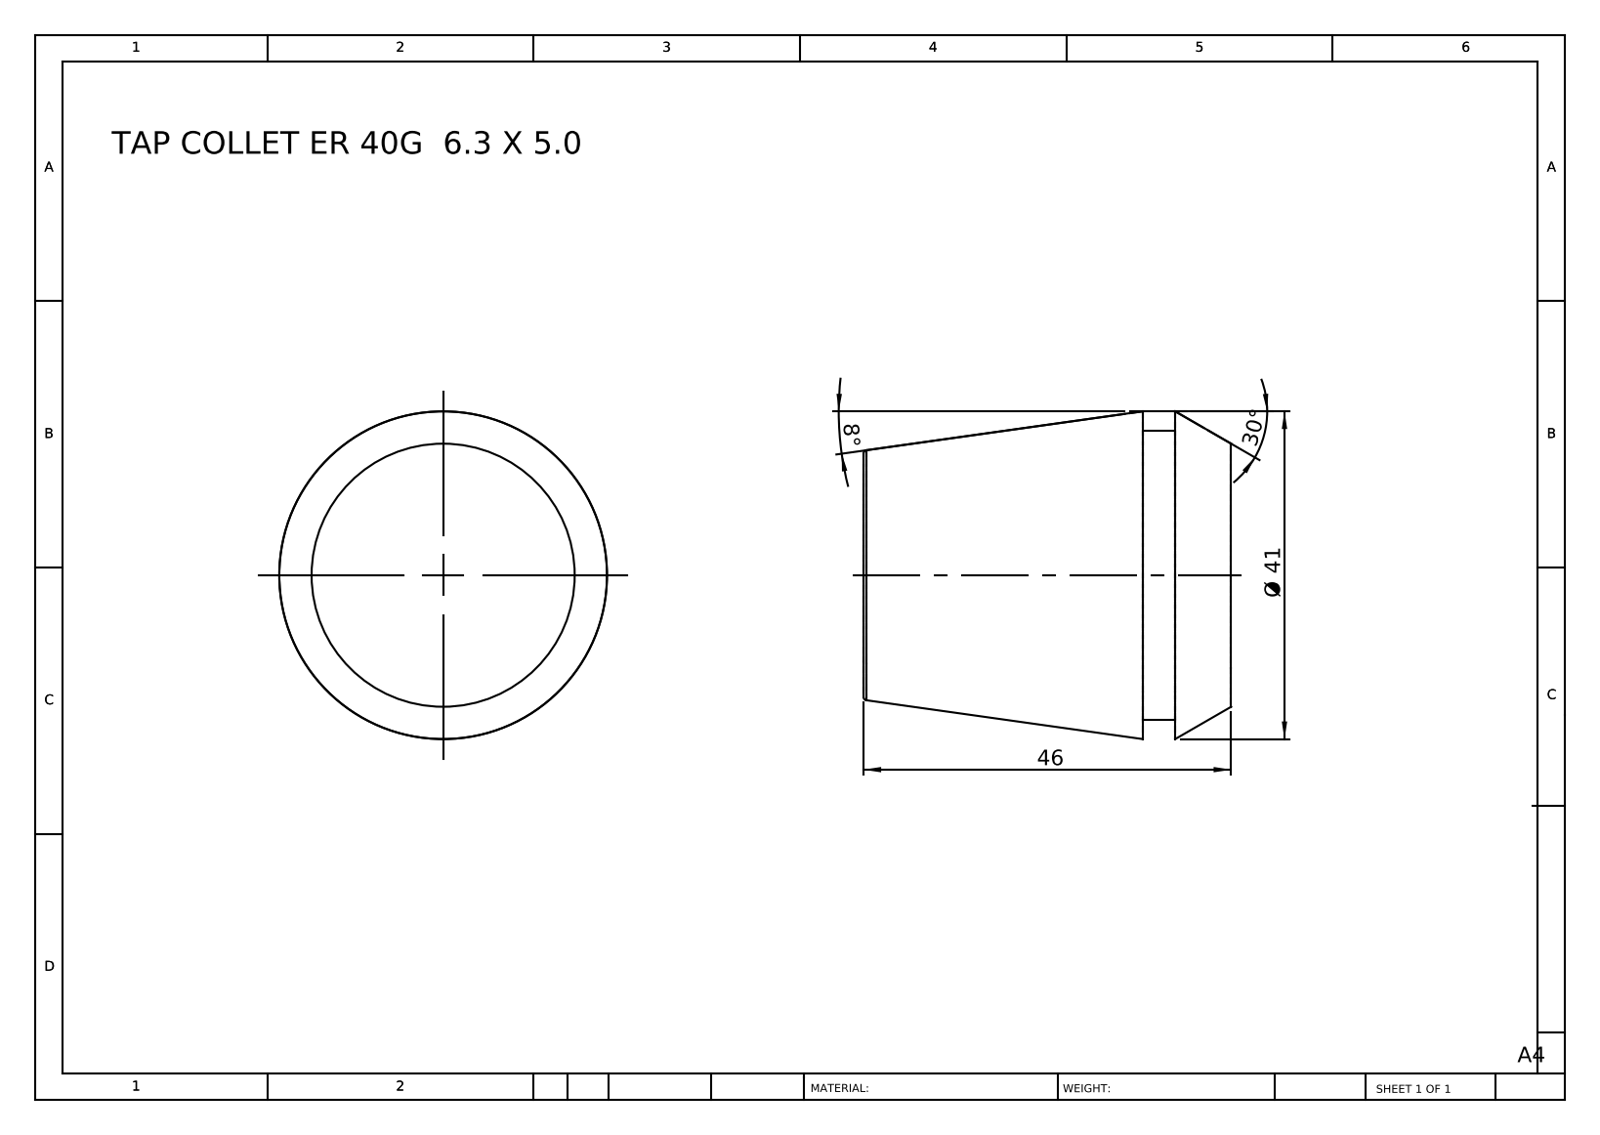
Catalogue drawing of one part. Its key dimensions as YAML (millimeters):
part_name: "TAP COLLET ER 40G 6.3 X 5.0"
step_written_by: "SolidWorks 2014 (CONFIG_CONTROL_DESIGN)"
units: millimeters
bodies: {solids: 1, faces: 12, planar: 4, cylindrical: 2, other: 6}
overall_size: [46, 41, 41]
volume: 47690
surface_area: 7586
round_bosses_or_shafts:
  - {diameter: 36.2, count: 1}
face_to_face_distances: [46, 11.1, 34.9, 7, 4.1, 39]
